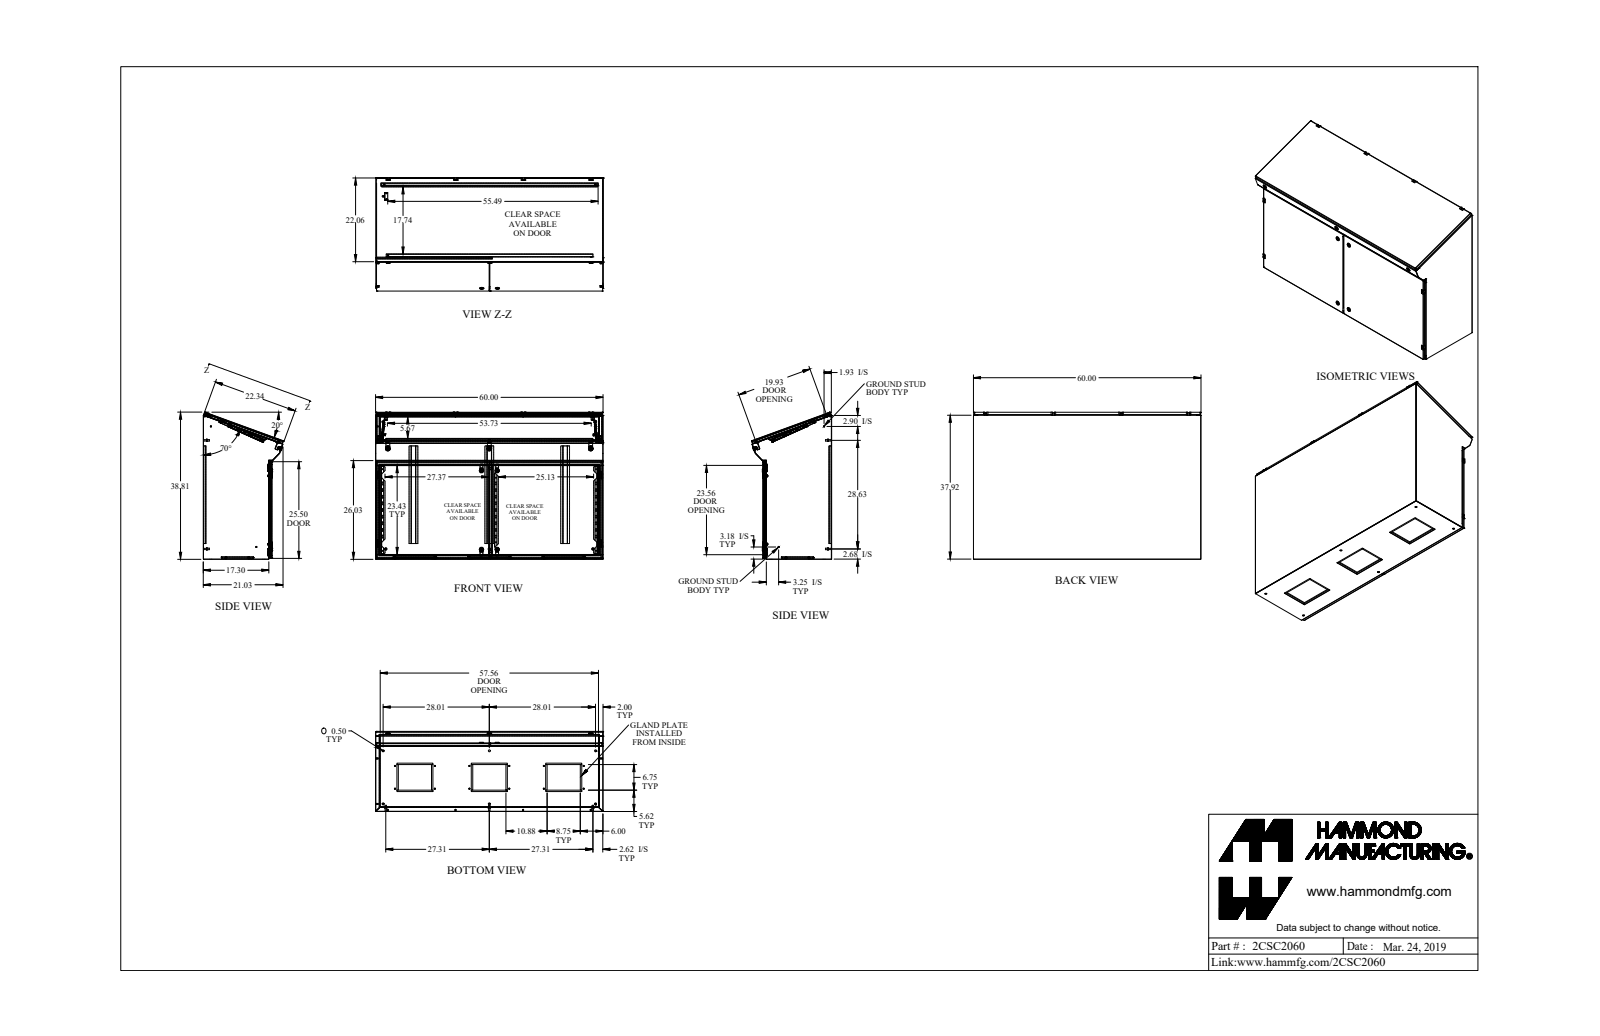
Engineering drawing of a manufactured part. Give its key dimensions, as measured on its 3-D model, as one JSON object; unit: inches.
{"part_name": "2CSC2060", "step_written_by": "SolidWorks 2018 (AUTOMOTIVE_DESIGN)", "units": "inches", "bodies": {"solids": 153, "faces": 3087, "planar": 2171, "cylindrical": 724, "other": 192}, "overall_size": [60, 38.809, 21.124], "volume_in3": 753.1, "surface_area_in2": 19480, "round_holes": [[0.281, 68], [0.5, 13], [0.196, 12], [0.189, 8], [0.197, 8], [0.313, 8], [0.197, 7], [0.387, 7], [0.63, 7], [0.768, 7], [0.391, 4], [0.25, 3]], "round_bosses_or_shafts": [[0.236, 19], [0.25, 17], [0.236, 15], [0.313, 10], [0.374, 8], [1.1, 7], [0.625, 7], [0.65, 6]], "partial_cylinders_radius": [[0.036, 61], [0.108, 61], [0.125, 36], [0.043, 12], [0.116, 12], [0.25, 12], [0.047, 8], [0.059, 8]], "face_to_face_distances": [0.072, 0.072, 18.014, 0.074, 17.945, 17.943, 0.069, 18.017, 18.089, 18.017], "hole_center_spacings": [1.75, 3.5, 5.25, 7, 10.5, 0.5, 1.25, 4]}
